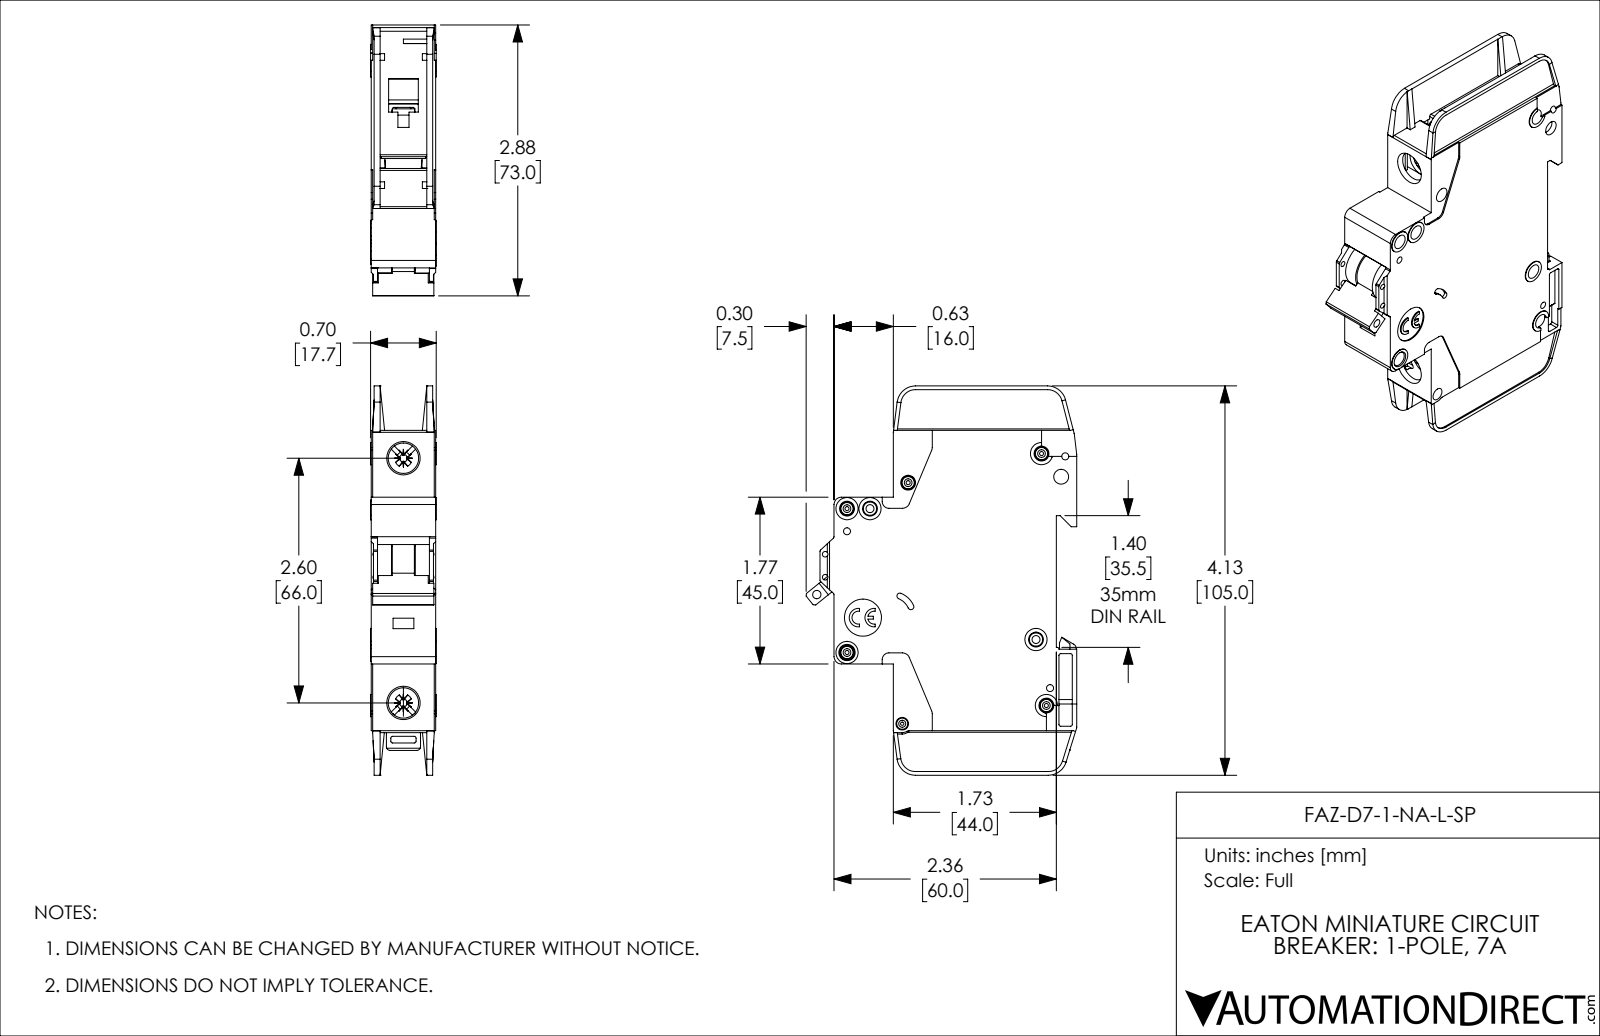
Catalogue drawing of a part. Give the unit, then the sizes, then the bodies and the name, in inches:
Units: inches
Overall size (bounding box): 4.134 × 2.876 × 0.697
Round holes (diameter × count): ⌀0.157 ×8, ⌀0.043 ×5, ⌀0.075 ×4, ⌀0.059 ×2, ⌀0.085 ×2, ⌀0.323 ×2, ⌀0.035 ×1, ⌀0.089 ×1, ⌀0.098 ×1, ⌀0.134 ×1, ⌀0.394 ×1
Round bosses / shafts (diameter × count): ⌀0.13 ×5, ⌀0.236 ×4, ⌀0.118 ×2, ⌀0.098 ×1
Partial cylindrical surfaces — rounded edges, fillets, slot ends (radius × count): R0.02 ×42, R0.016 ×10, R0.039 ×10, R0.079 ×8, R0.197 ×5, R0.008 ×4, R0.026 ×4, R0.043 ×4
Main face-to-face distances: 0.047, 0.685, 0.591, 0.638, 0.094, 0.543, 0.016, 0.031, 0.496, 0.575
Hole centre spacings: 0.244, 0.537, 0.87, 0.189, 0.199, 0.204, 0.221, 0.24
Volume: 4.682 in³ · Surface area: 41.01 in²
Bodies: 1 solid, 1127 faces (671 planar, 357 cylindrical, 99 other)
Part name (STEP PRODUCT): FAZ-D7-1-NA-L-SP
STEP written by: SolidWorks 2019 (AUTOMOTIVE_DESIGN)
